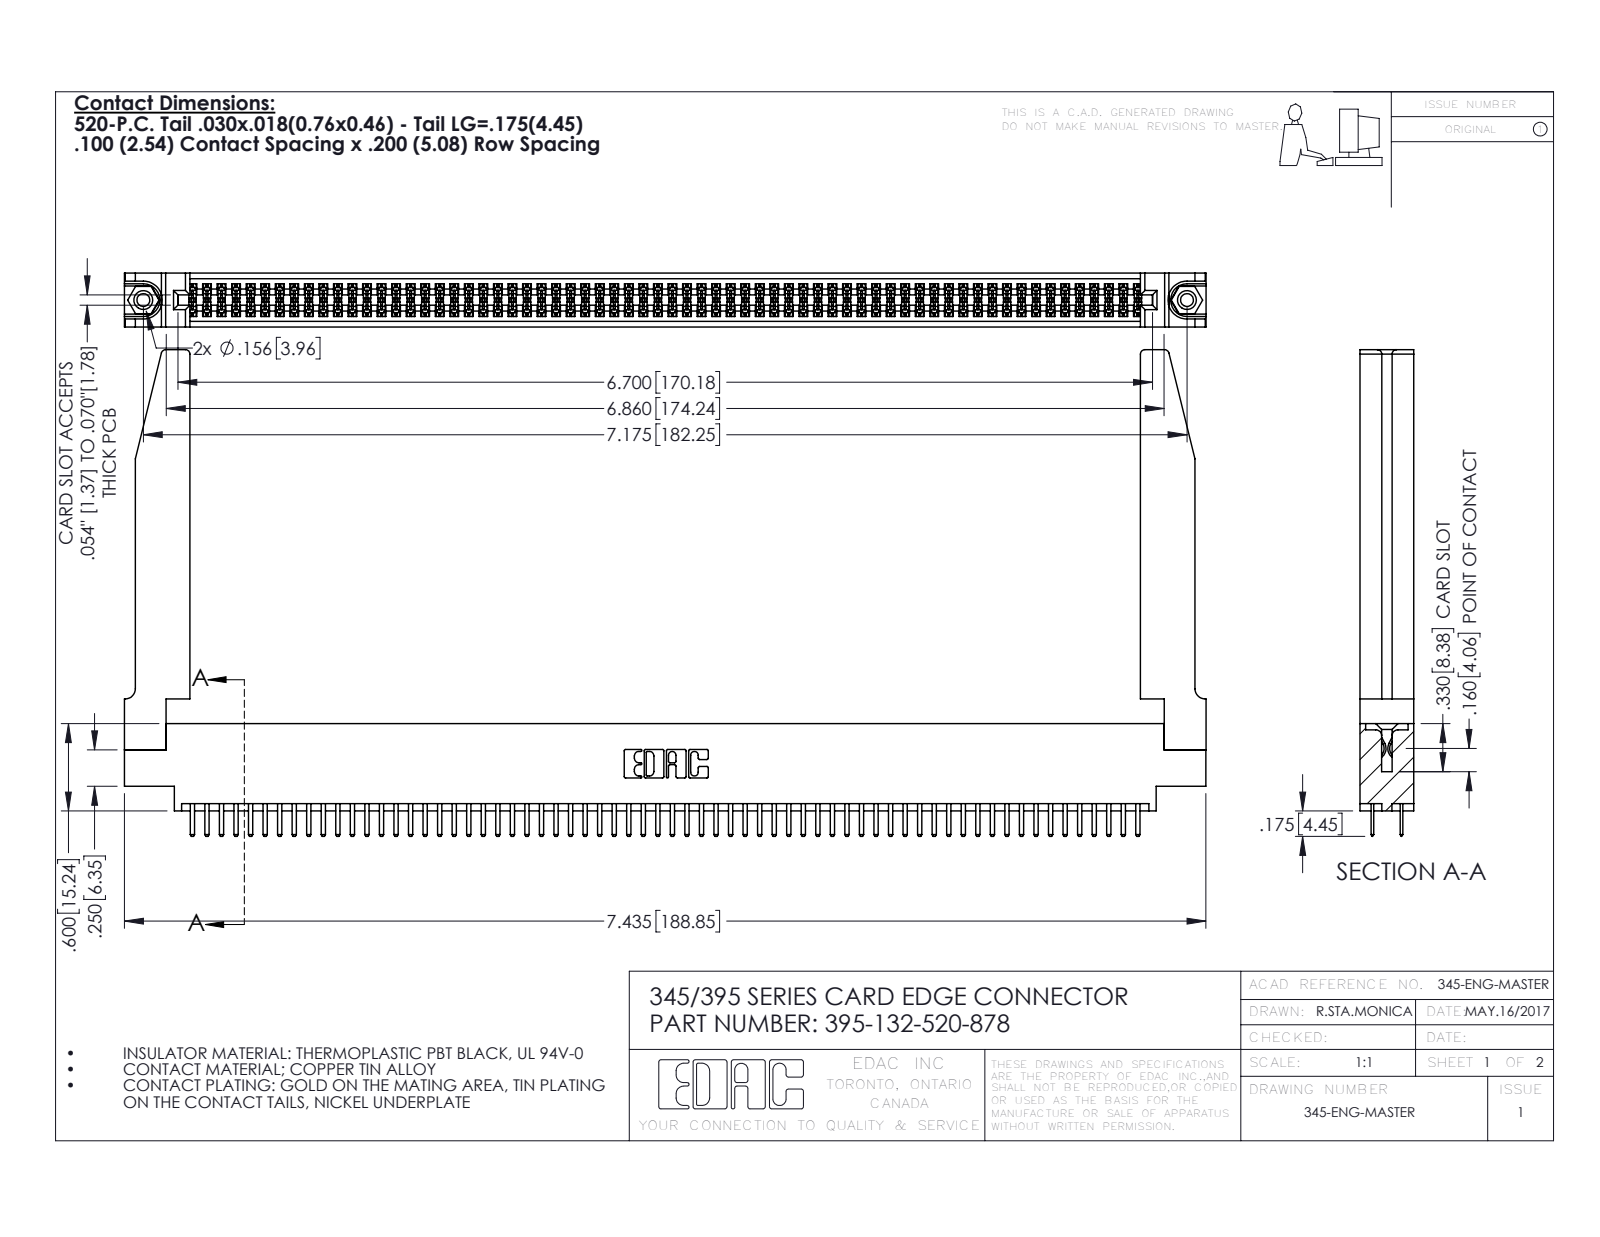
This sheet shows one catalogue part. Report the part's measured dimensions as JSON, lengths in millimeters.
{"part_name": "345-250-001_345-250-001-102; 345 Part_0.170 Offset - 0.156 Dia-TH; 395-132-520-878; 345-220-078_345-220-078 (+1 more)", "step_written_by": "SolidWorks 2016 (CONFIG_CONTROL_DESIGN)", "units": "millimeters", "bodies": {"solids": 137, "faces": 7492, "planar": 4846, "cylindrical": 2594, "other": 52}, "overall_size": [188.9, 85, 9.4], "volume_mm3": 26170, "surface_area_mm2": 34520, "round_holes": [[2.3, 2], [3.2, 2], [4, 2], [1.6, 1]], "round_bosses_or_shafts": [[3.9, 2]], "partial_cylinders_radius": [[0.2, 198], [0.3, 136], [0.3, 22], [0.8, 8], [0.2, 6], [0.8, 6], [0.7, 3], [0.4, 2]], "face_to_face_distances": [1.8, 9.4, 7.6, 5.1, 2.5, 6.9, 0.6, 5.7, 0.6, 1.8], "hole_center_spacings": [6.9, 176.3, 182.2]}
